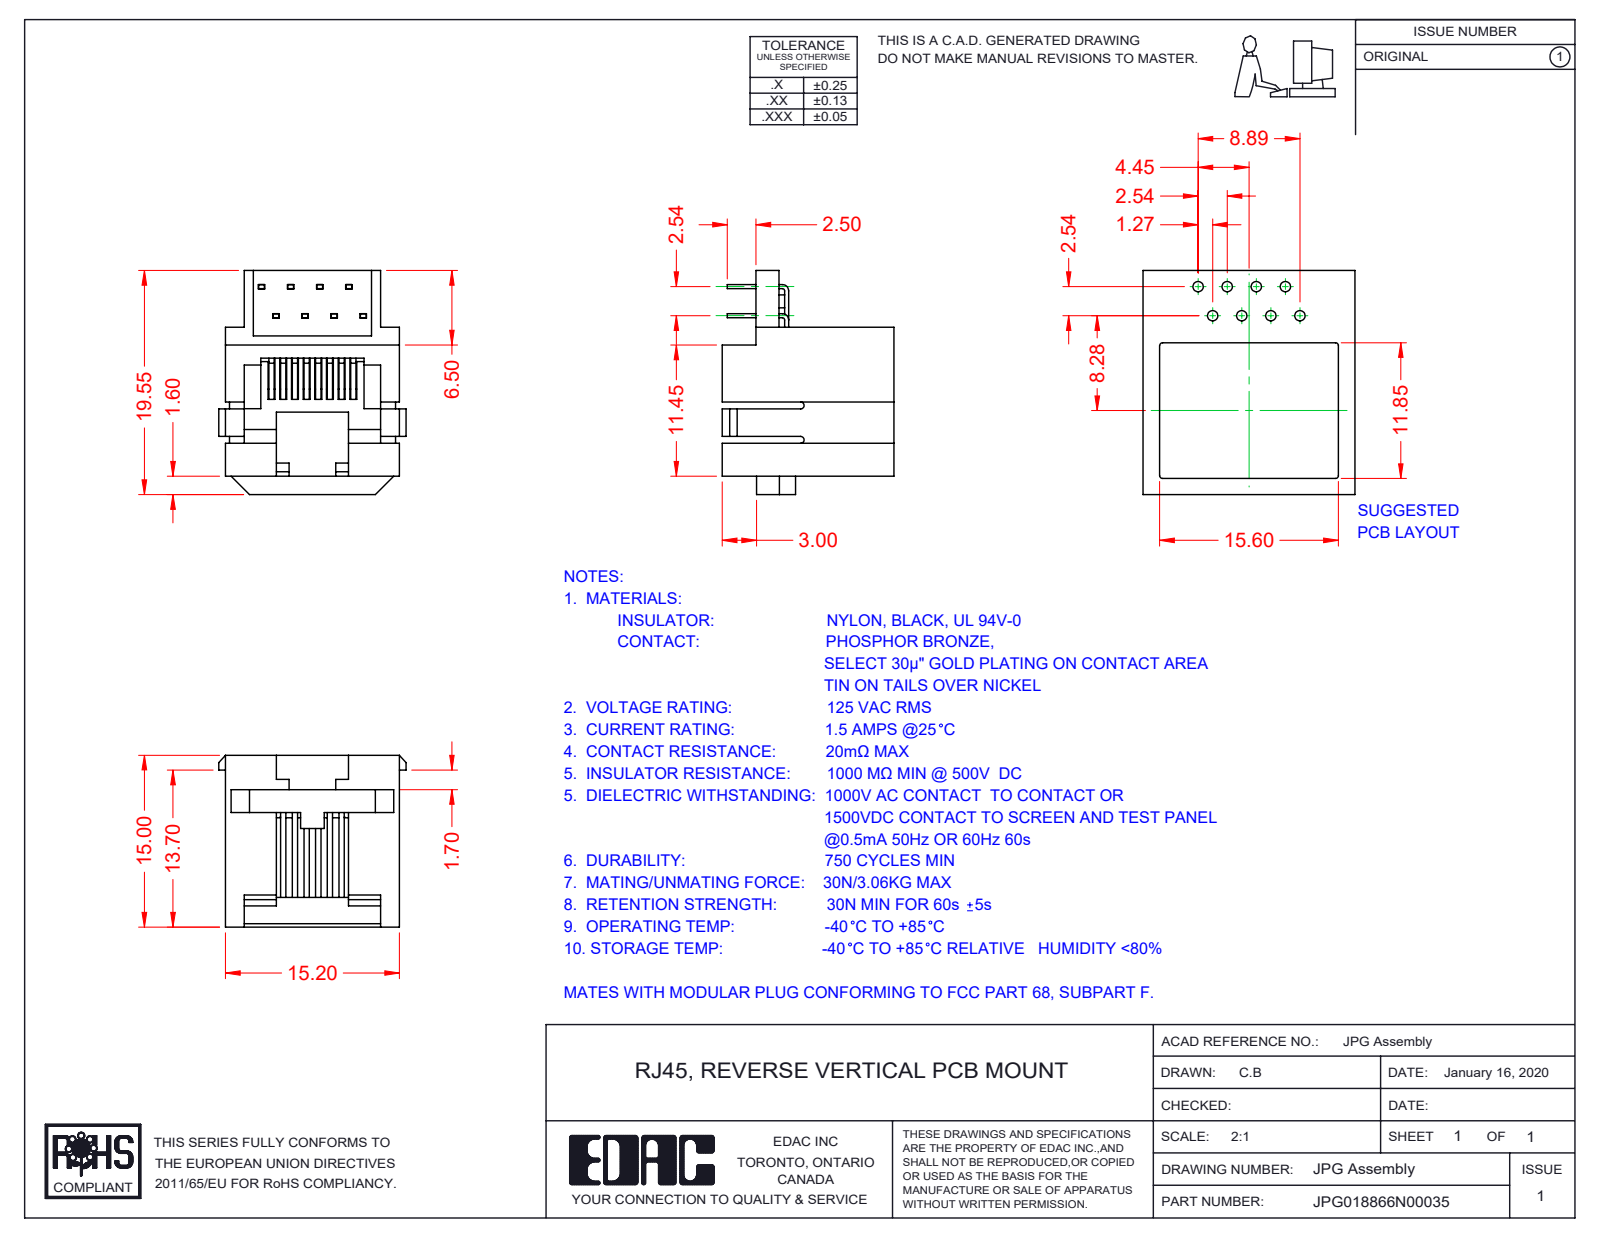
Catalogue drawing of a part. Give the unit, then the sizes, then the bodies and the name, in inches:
Units: inches
Overall size (bounding box): 0.77 × 0.644 × 0.591
Partial cylindrical surfaces — rounded edges, fillets, slot ends (radius × count): R0.012 ×3, R0.008 ×2, R0.014 ×2, R0.022 ×2, R0.028 ×2
Main face-to-face distances: 0.014, 0.065, 0.534, 0.406, 0.598, 0.102, 0.071, 0.024, 0.053, 0.508
Volume: 0.085 in³ · Surface area: 4.196 in²
Bodies: 10 solids, 542 faces (461 planar, 69 cylindrical, 12 other)
Part name (STEP PRODUCT): PG Contact Lock; JPG018866N00035; PG Insulator; PG Contacts
STEP written by: SolidWorks 2016 (CONFIG_CONTROL_DESIGN)
